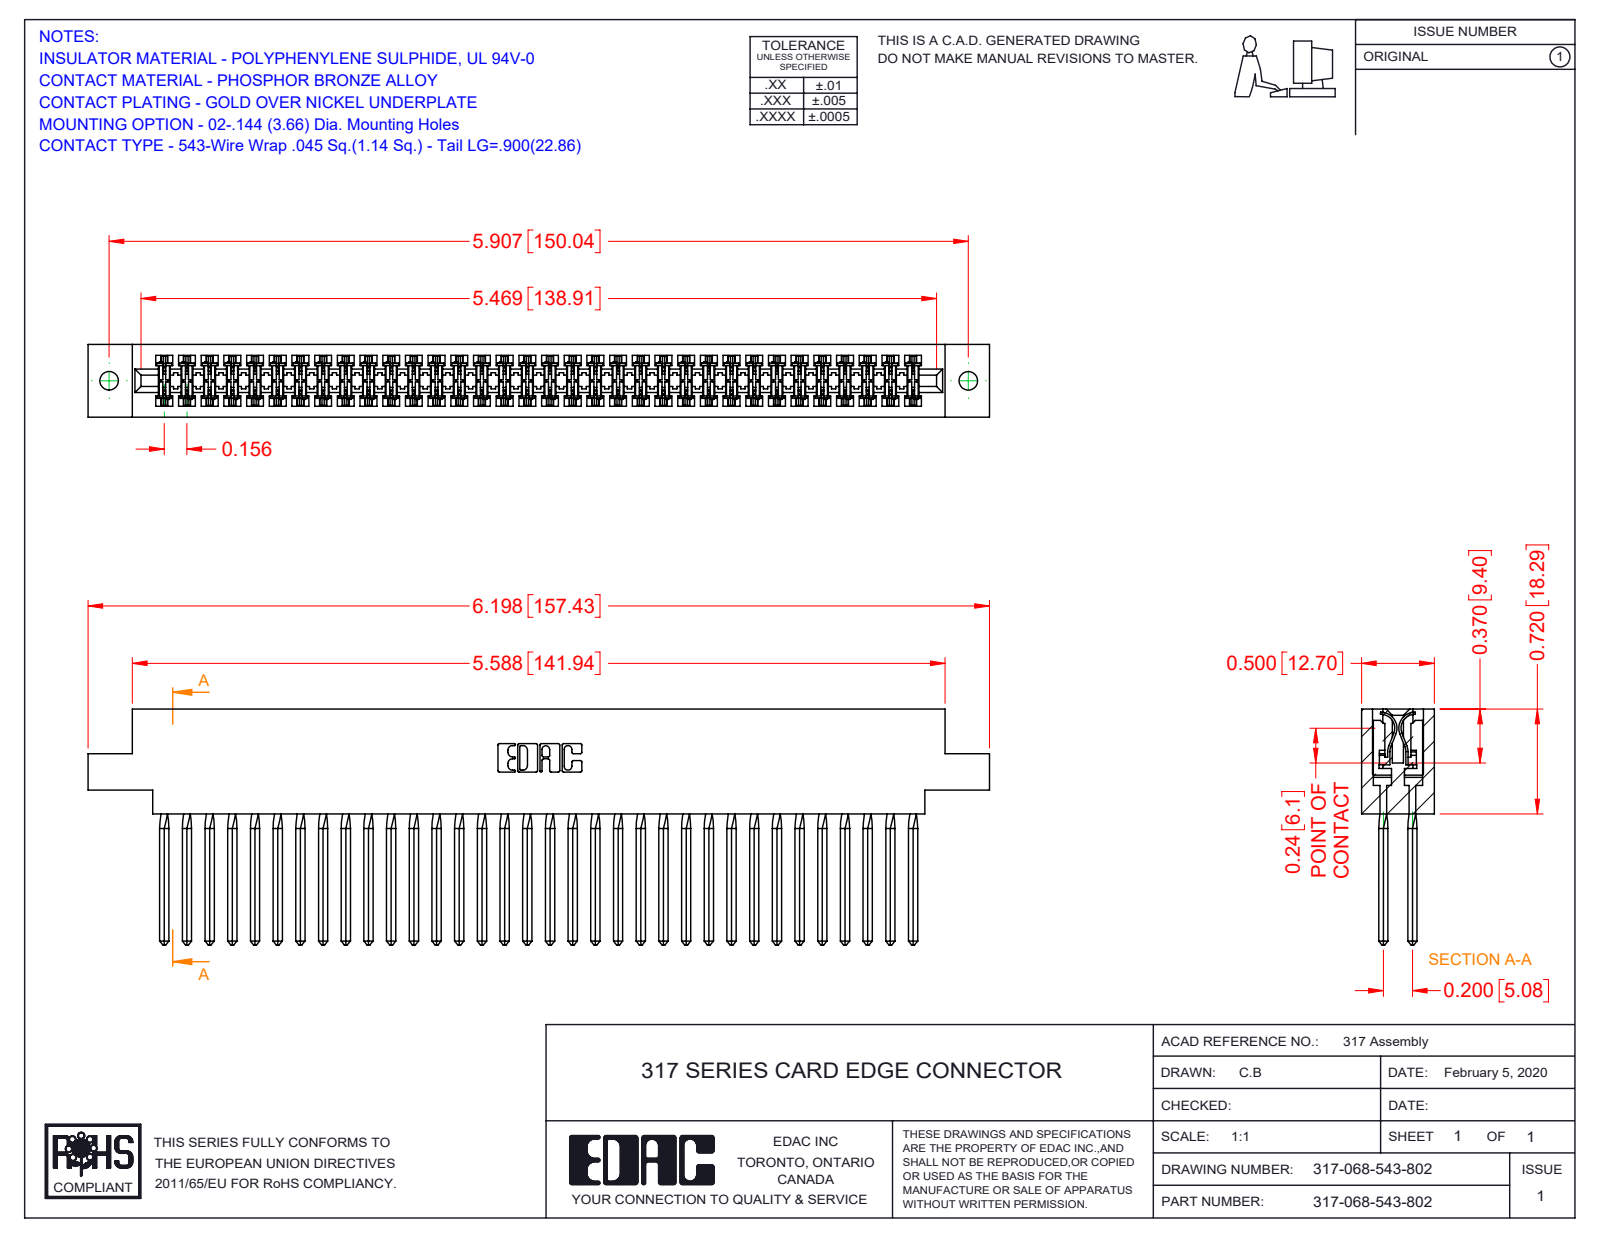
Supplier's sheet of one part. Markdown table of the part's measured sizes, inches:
| quantity | value |
| --- | --- |
| part name | 317-290-001_543; 317-068-543-802; 317 Part_.144 Dia |
| STEP written by | SolidWorks 2016 (CONFIG_CONTROL_DESIGN) |
| units | inches |
| bodies | 69 solids, 6154 faces (5022 planar, 860 cylindrical, 272 other) |
| overall size | 6.198 × 1.62 × 0.5 |
| volume | 1.614 in³ |
| surface area | 61.31 in² |
| round holes (diameter × count) | 0.128 × 2 |
| partial cylindrical surfaces (radius × count) | 0.015 × 136, 0.01 × 22, 0.007 × 6, 0.031 × 6, 0.026 × 3, 0.095 × 2, 0.1 × 2, 0.11 × 2 |
| main face-to-face distances | 0.5, 0.075, 0.425, 0.35, 0.11, 0.195, 0.094, 0.2, 0.115, 0.131 |
| hole center spacings | 5.907 |
